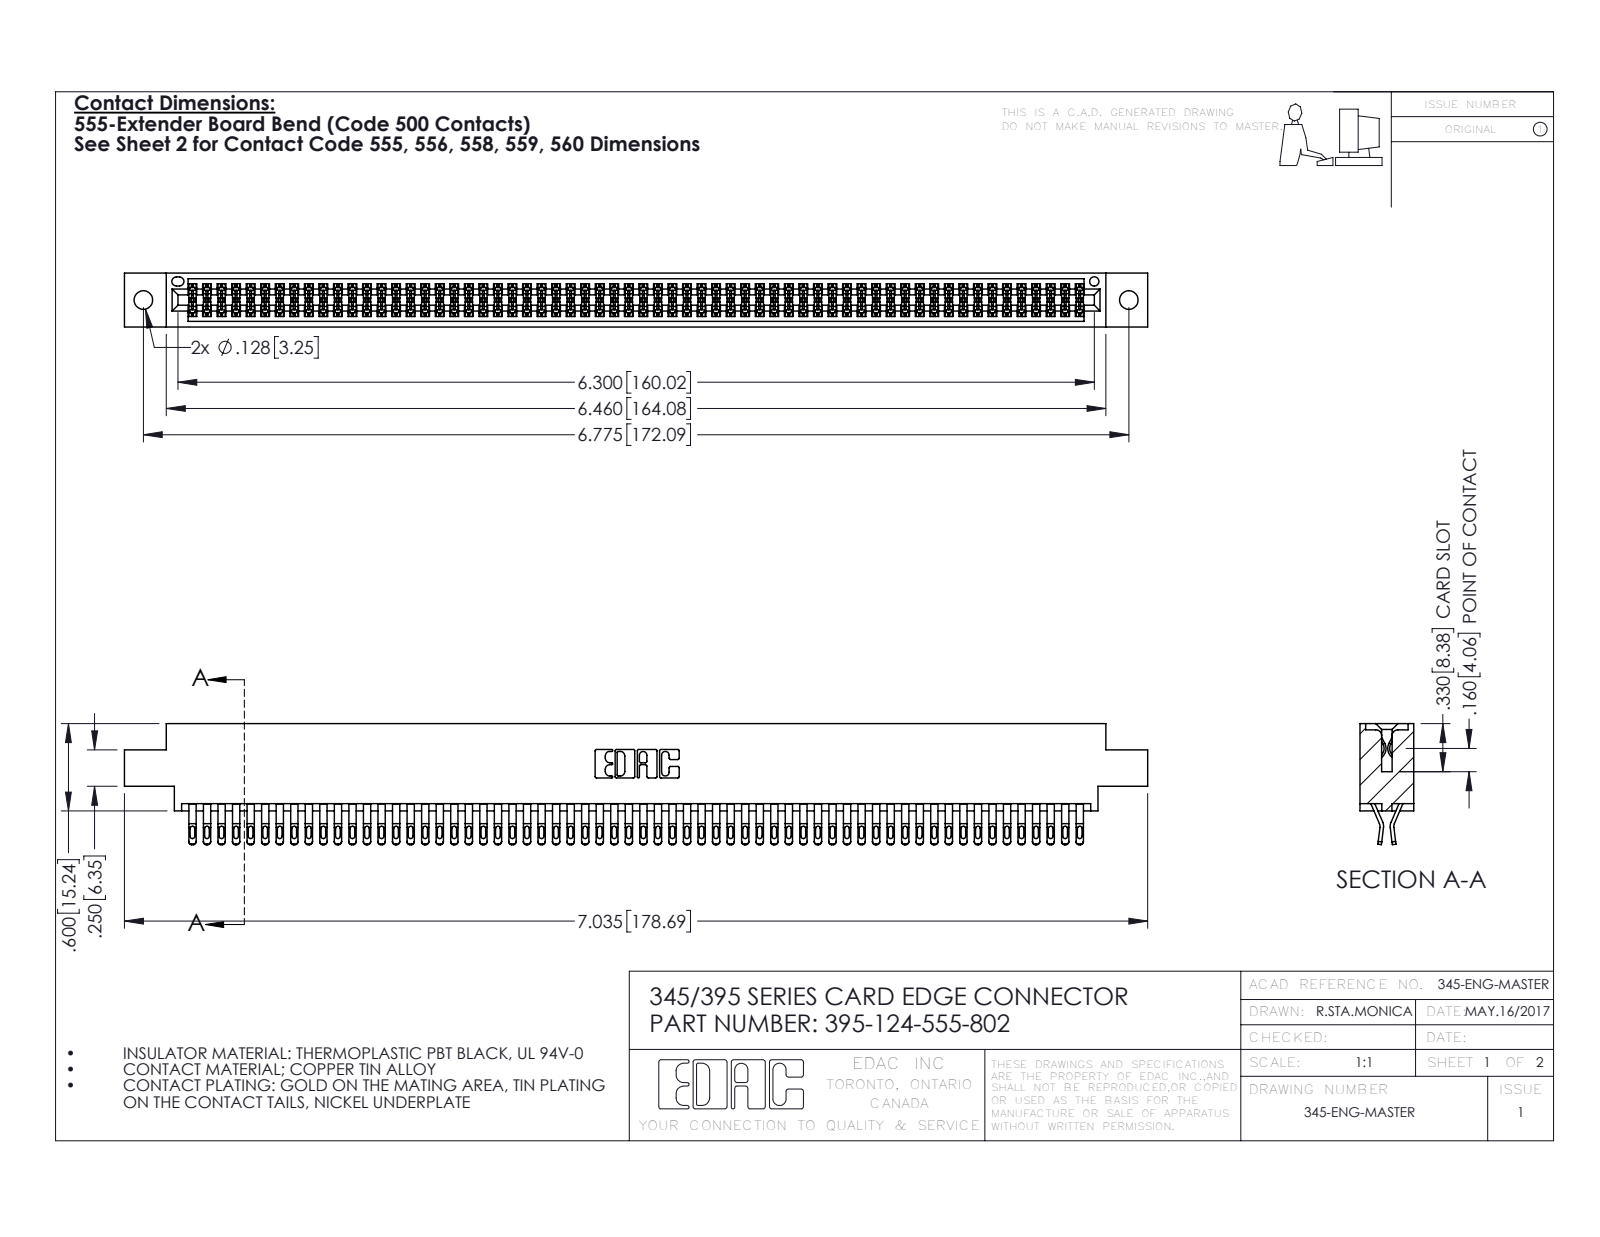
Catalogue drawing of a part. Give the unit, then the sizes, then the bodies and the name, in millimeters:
Units: millimetres
Overall size (bounding box): 178.7 × 21.1 × 9.4
Round holes (diameter × count): ⌀3.3 ×2, ⌀1.6 ×1
Partial cylindrical surfaces — rounded edges, fillets, slot ends (radius × count): R0.4 ×310, R0.5 ×248, R0.2 ×186, R0.3 ×22, R0.2 ×6, R0.8 ×6, R0.7 ×3, R0.3 ×2
Main face-to-face distances: 7.6, 1.8, 9.4, 0.6, 5.1, 2.5, 6.9, 5.7, 4.4, 3.8
Hole centre spacings: 6.9, 166.1, 172.1
Volume: 17 750 mm³ · Surface area: 27 750 mm²
Bodies: 125 solids, 7074 faces (3928 planar, 3146 cylindrical, 0 other)
Part name (STEP PRODUCT): 395-124-555-802; 345 Part_0.170 Offset - 0.128 Dia; 345-292-001_555 Tail
STEP written by: SolidWorks 2016 (CONFIG_CONTROL_DESIGN)
